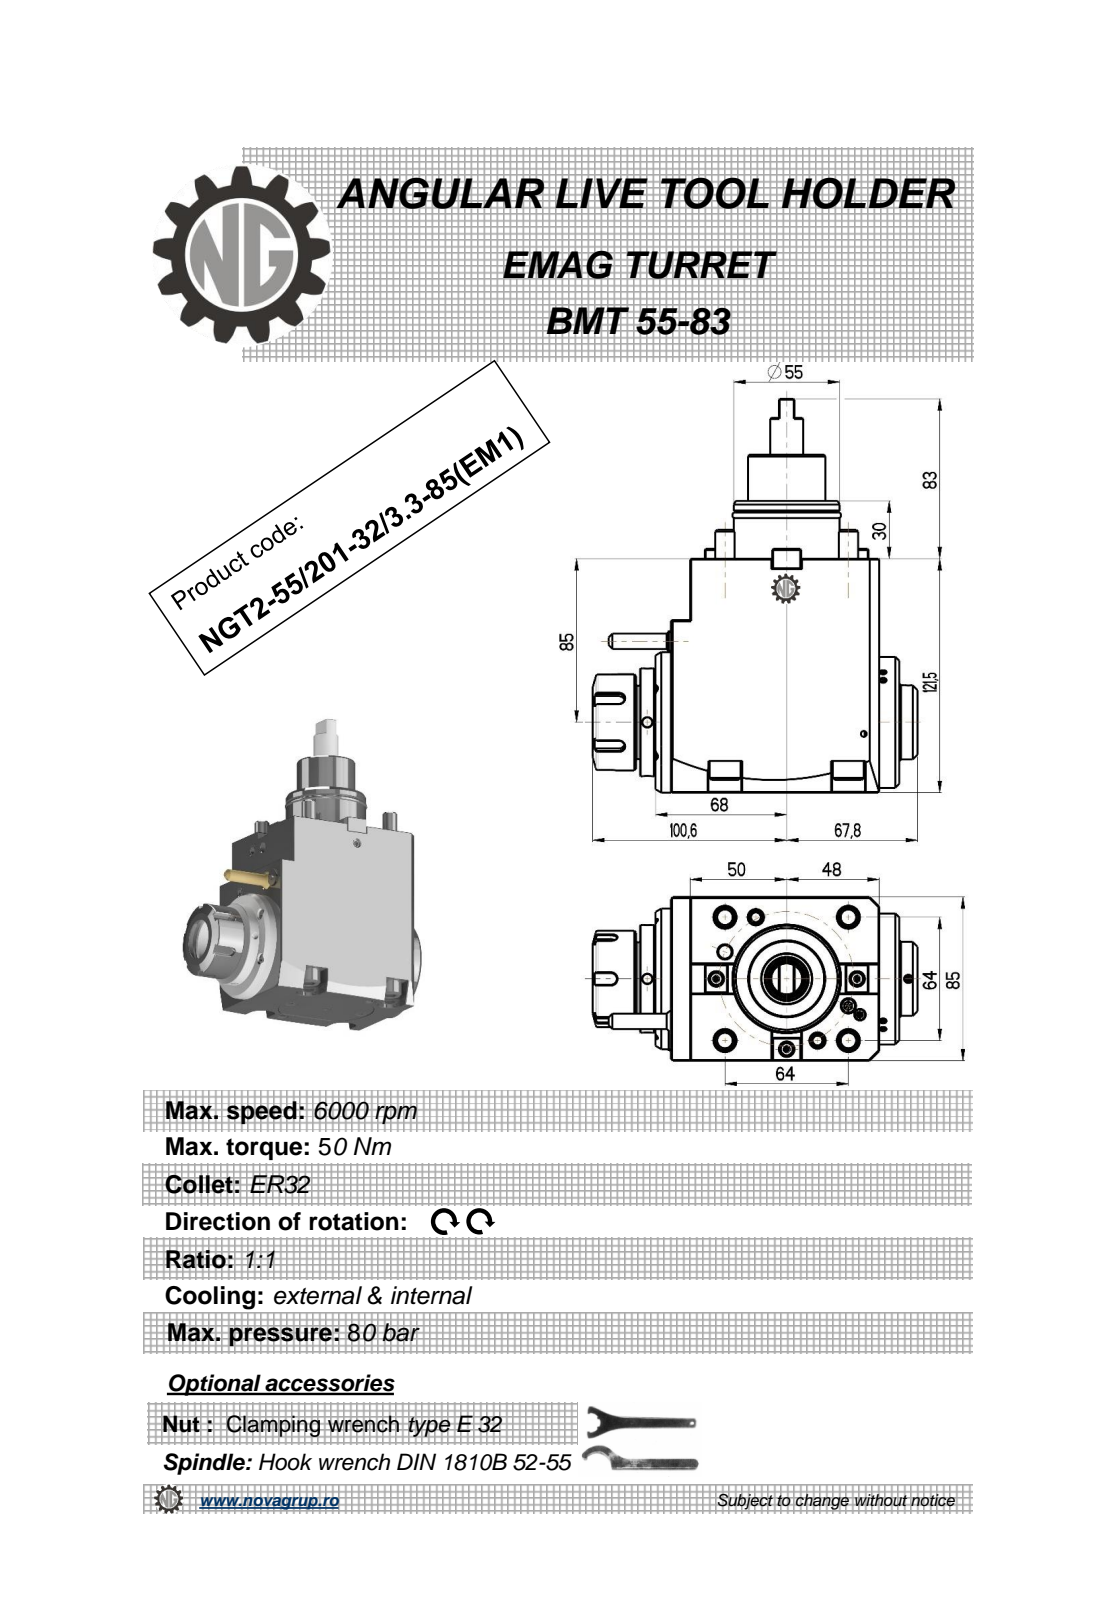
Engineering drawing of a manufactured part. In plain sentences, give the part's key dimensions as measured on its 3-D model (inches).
The part is named "NGT2_55_201_32_3_3_85_EM1". Its 3-D file was written by "PRO/ENGINEER BY PARAMETRIC TECHNOLOGY CORPORATION, 2010280 (CONFIG_CONTROL_DESIGN)". It is 2 solids with 502 faces: 242 planar, 119 cylindrical and 141 other. Overall it measures 8.051 by 6.63 by 3.346 inches. Its volume is 80.12 cubic inches and its surface area 176.1 square inches. Round holes: 3 of diameter 0.197, 2 of diameter 0.268, 1 of diameter 0.118, 1 of diameter 0.472, 1 of diameter 1.063. Round bosses or shafts: 4 of diameter 0.63, 4 of diameter 0.394, 2 of diameter 1.969, 1 of diameter 2.874, 1 of diameter 2.677, 1 of diameter 2.205, 1 of diameter 2.165, 1 of diameter 1.709. Partial cylindrical surfaces (rounded edges, fillets, slot ends): 20 of radius 0.013, 6 of radius 0.009, 6 of radius 0.012, 5 of radius 0.118, 4 of radius 0.335, 2 of radius 0.031, 2 of radius 18.898. The main face-to-face distances are 3.346, 4.783, 0.315, 0.394, 4.252, 0.709, 3.858, 4.567, 4.264, 4.972. The hole center spacings are 1.678, 1.867, 2.75, 4.141.
